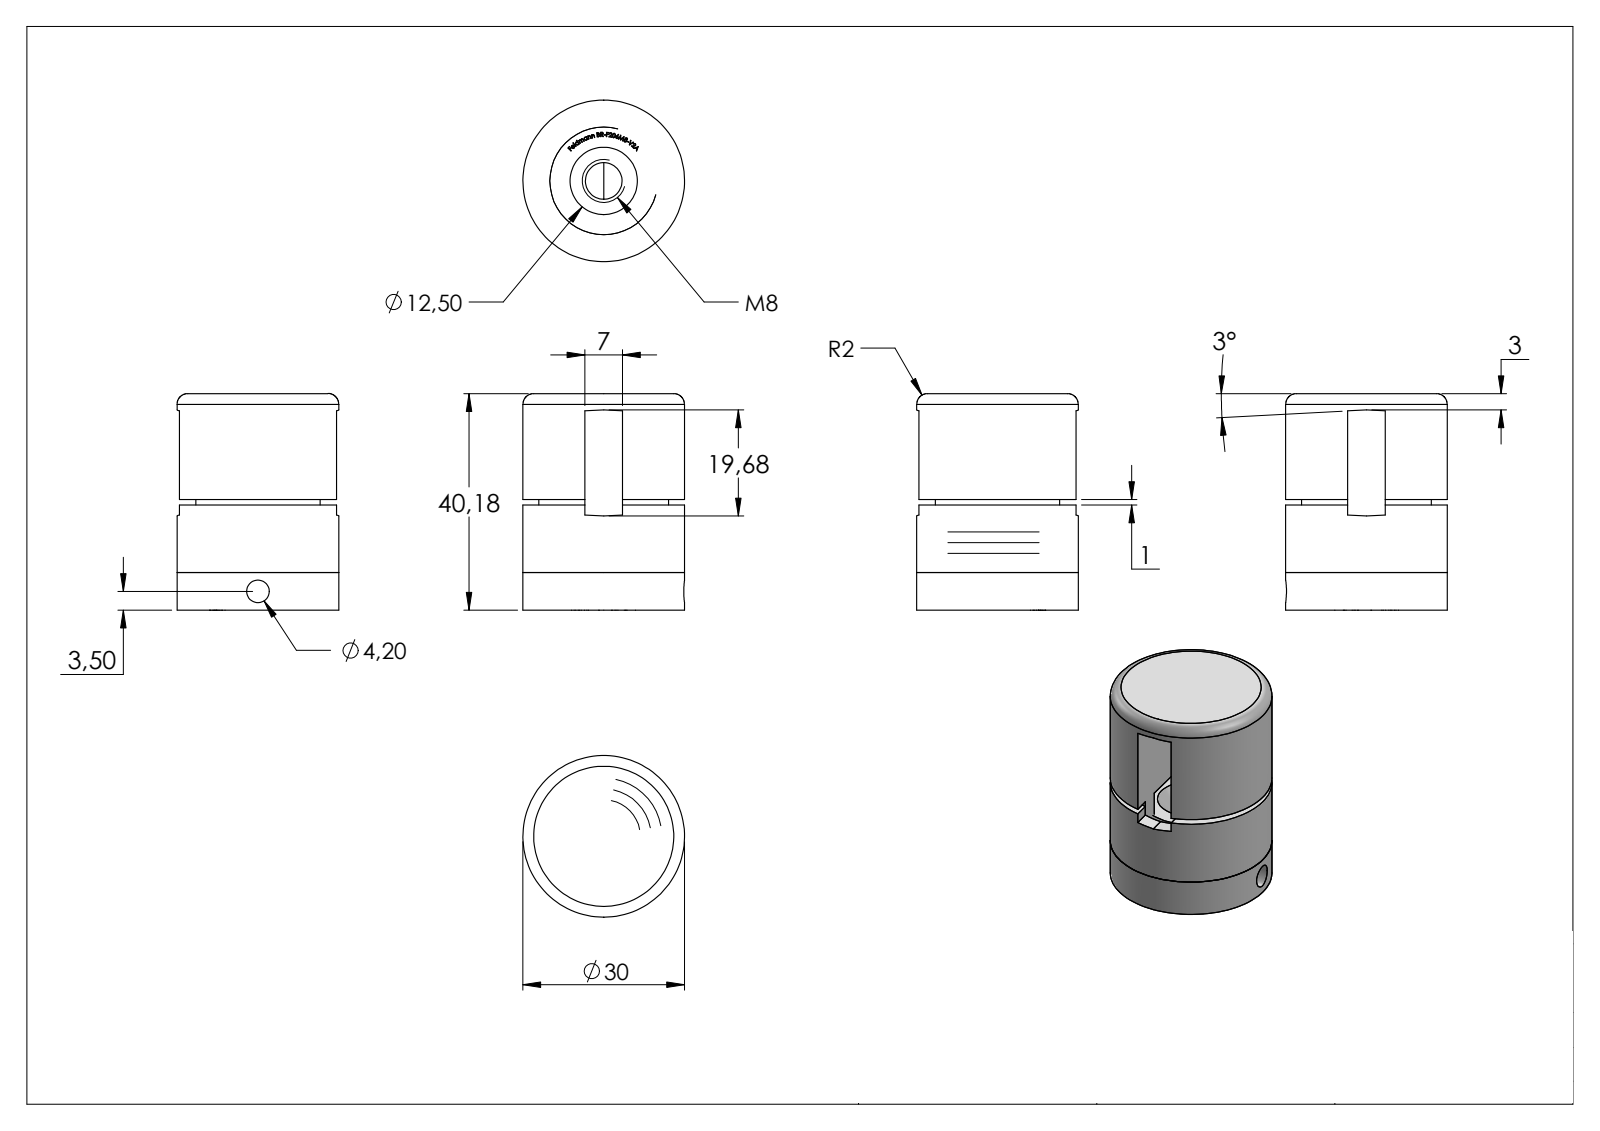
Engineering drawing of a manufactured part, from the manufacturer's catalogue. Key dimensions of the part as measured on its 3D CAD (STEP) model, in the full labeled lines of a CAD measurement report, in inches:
Part name (STEP PRODUCT): BR-R1XM8-XXX Teil1; BR-R1XM8-XXX Teil1_BR-FXXXM8-V2A Teil1; BR-R1XM8-XXX Teil3; BR-R1XM8-XXX Teil2_BR-F206M8-V2A Teil2 (+3 more)
STEP written by: SolidWorks 2015 (CONFIG_CONTROL_DESIGN)
Units: inches
Bodies: 3 solids, 323 faces (197 planar, 12 cylindrical, 114 other)
Overall size (bounding box): 2.533 × 1.181 × 1.181
Volume: 1.35 in³ · Surface area: 16.9 in²
Round holes (diameter × count): ⌀0.165 ×1, ⌀0.268 ×1, ⌀0.492 ×1, ⌀0.953 ×1
Round bosses / shafts (diameter × count): ⌀1.181 ×1, ⌀0.949 ×1, ⌀0.787 ×1
Partial cylindrical surfaces — rounded edges, fillets, slot ends (radius × count): R0.344 ×1
Main face-to-face distances: 0.276, 1.582, 1.306, 0.808, 0.533, 0.774, 0.039, 0.493, 0.315, 0.769
